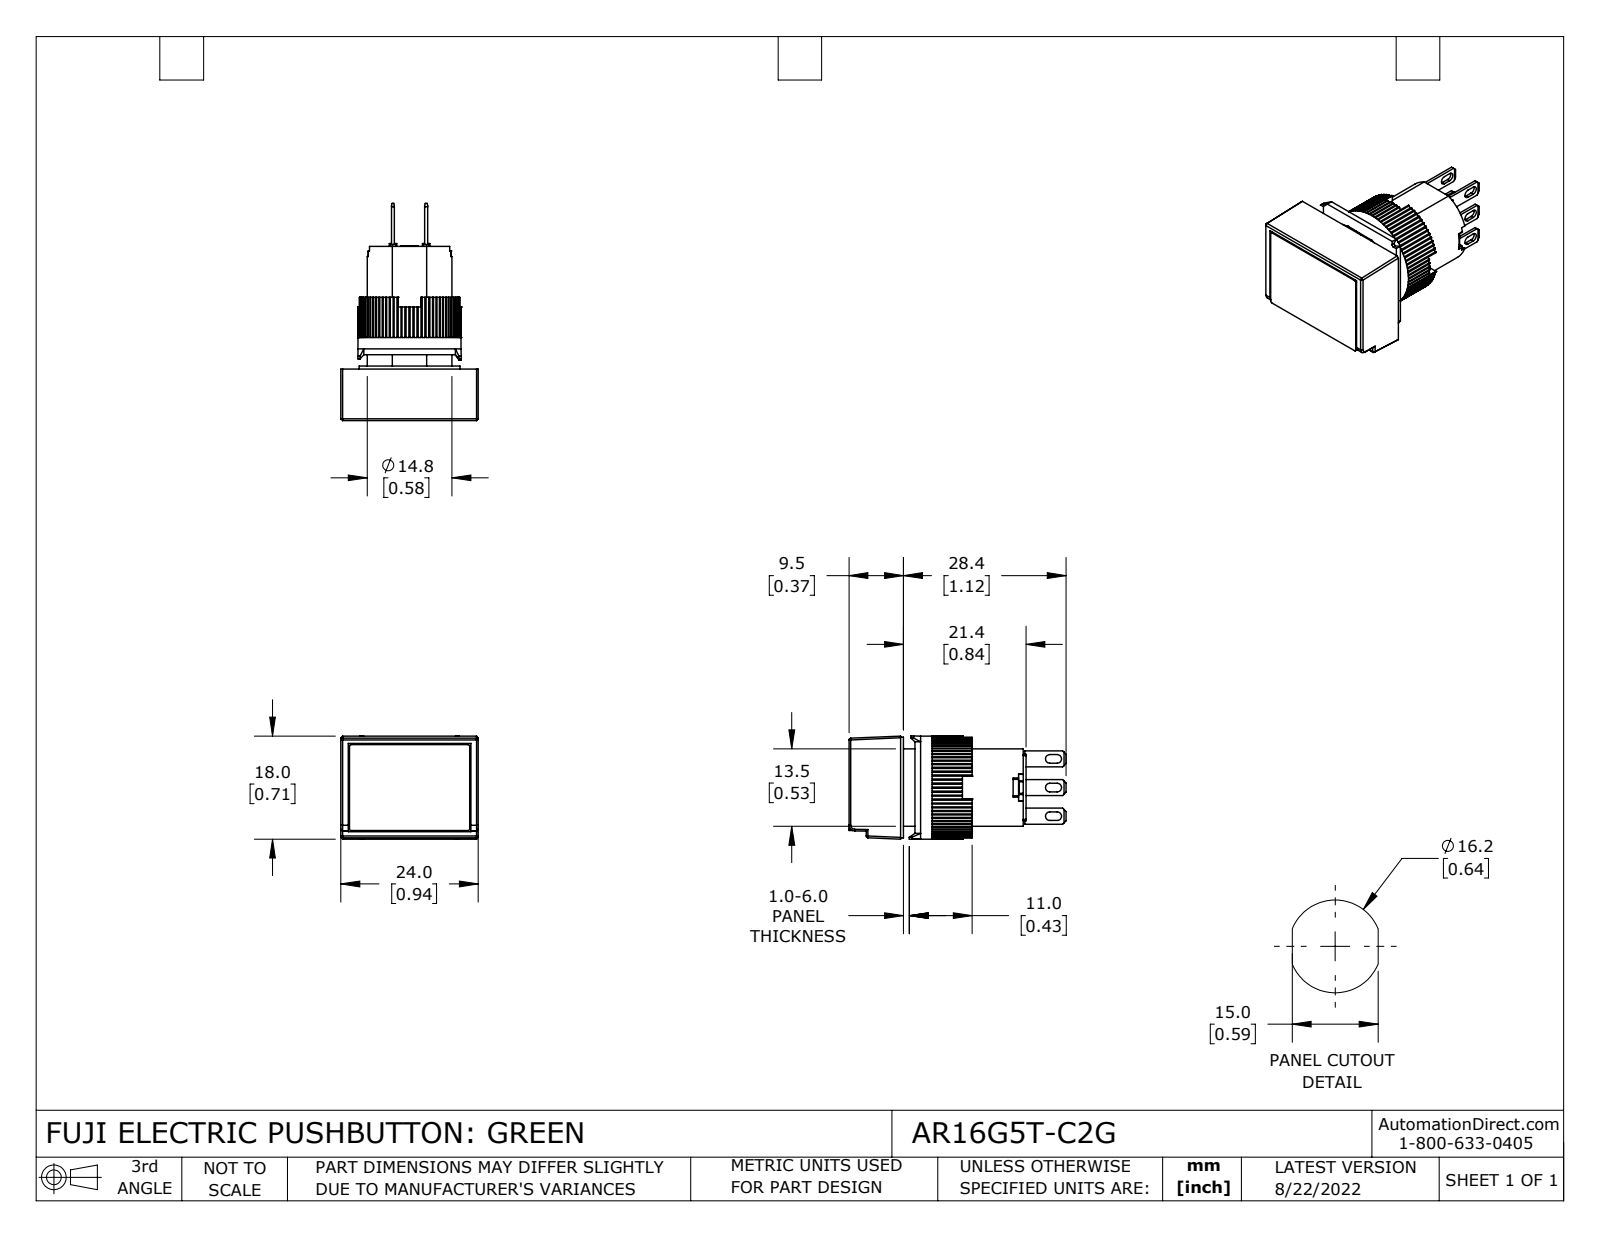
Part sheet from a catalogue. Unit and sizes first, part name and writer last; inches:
Units: inches
Overall size (bounding box): 1.492 × 0.945 × 0.709
Round holes (diameter × count): ⌀0.543 ×1, ⌀0.583 ×1
Round bosses / shafts (diameter × count): ⌀0.709 ×1, ⌀0.693 ×1
Partial cylindrical surfaces — rounded edges, fillets, slot ends (radius × count): R0.01 ×80, R0.008 ×12, R0.012 ×6, R0.03 ×6, R0.039 ×1
Main face-to-face distances: 0.213, 0.354, 0.142, 0.492, 0.35, 0.138, 0.02, 0.843, 0.059, 0.453
Volume: 0.447 in³ · Surface area: 9.321 in²
Bodies: 12 solids, 811 faces (630 planar, 175 cylindrical, 6 other)
Part name (STEP PRODUCT): AR16G5T-C2G
STEP written by: SolidWorks 2021 (CONFIG_CONTROL_DESIGN)
